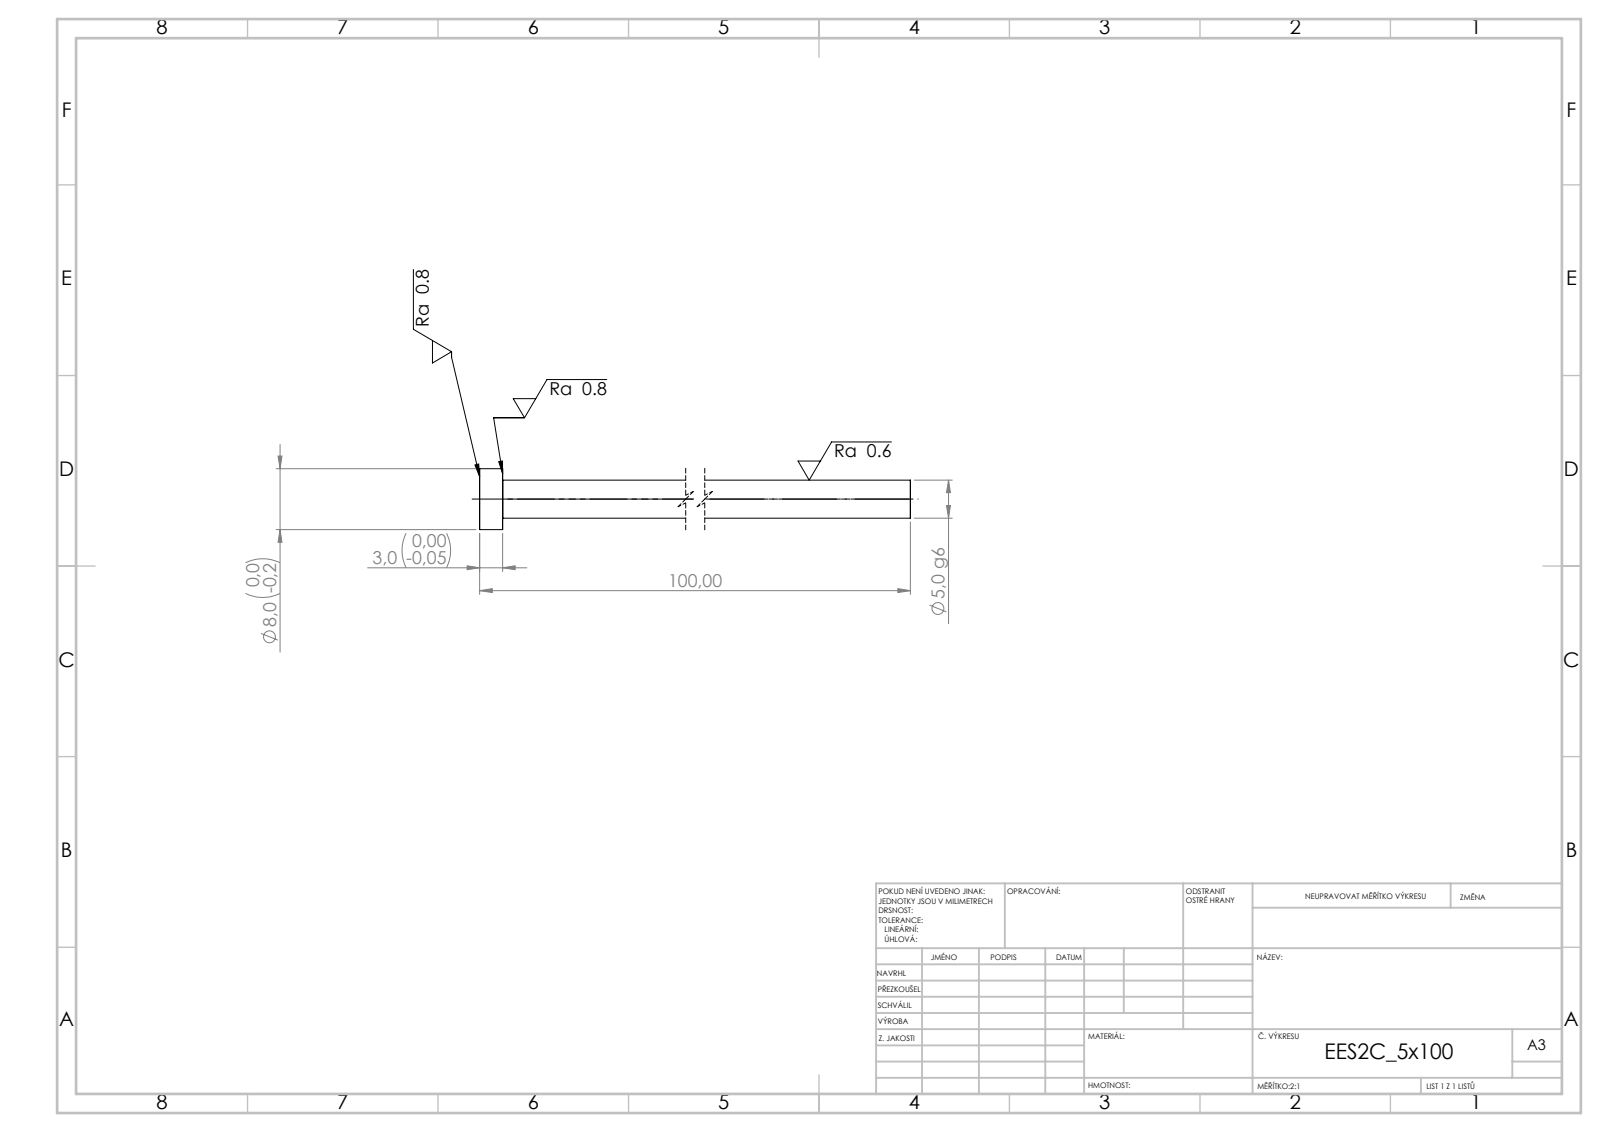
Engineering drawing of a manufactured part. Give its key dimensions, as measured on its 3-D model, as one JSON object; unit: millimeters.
{"step_written_by": "SolidWorks 2019 (CONFIG_CONTROL_DESIGN)", "units": "millimeters", "bodies": {"solids": 1, "faces": 9, "planar": 3, "cylindrical": 4, "other": 2}, "overall_size": [103, 10, 10], "volume_mm3": 2199, "surface_area_mm2": 1821, "round_bosses_or_shafts": [[10, 1], [5, 1]], "face_to_face_distances": [3, 103, 100]}
